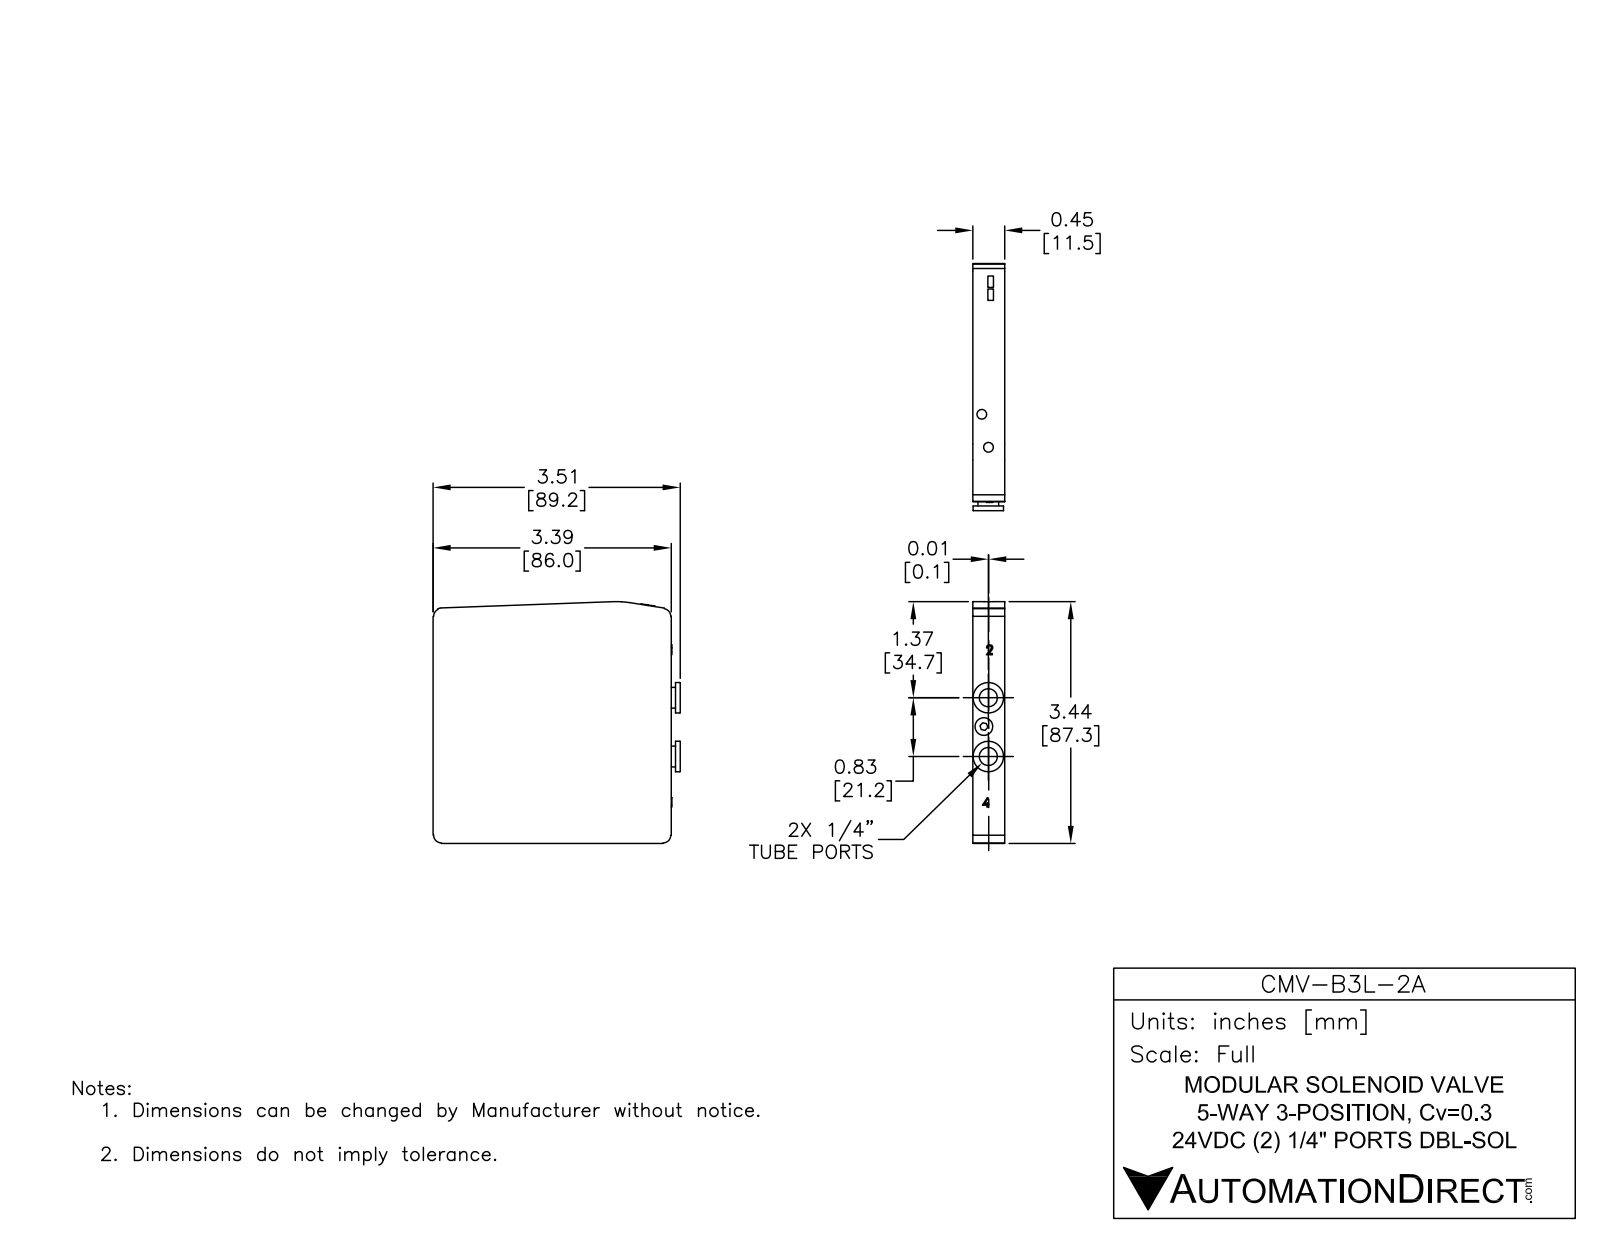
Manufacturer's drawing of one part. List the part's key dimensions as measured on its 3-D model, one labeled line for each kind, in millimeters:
Part name (STEP PRODUCT): CMV-B3L-2A
STEP written by: SolidWorks 2013 (AUTOMOTIVE_DESIGN)
Units: millimetres
Bodies: 78 solids, 1157 faces (879 planar, 162 cylindrical, 116 other)
Overall size (bounding box): 89.5 × 87.3 × 20.43
Volume: 78 068 mm³ · Surface area: 44 224 mm²
Round holes (diameter × count): ⌀5.25 ×4, ⌀6.5 ×4, ⌀3.35 ×2, ⌀4.4 ×2, ⌀8 ×2, ⌀9.5 ×2, ⌀3.6 ×1, ⌀6.25 ×1, ⌀6.4 ×1
Round bosses / shafts (diameter × count): ⌀1.5 ×4, ⌀10.8 ×2, ⌀7.75 ×2, ⌀6.25 ×2, ⌀5.75 ×2, ⌀4.2 ×2, ⌀4 ×2, ⌀3.5 ×1
Partial cylindrical surfaces — rounded edges, fillets, slot ends (radius × count): R2.35 ×12, R0.78 ×4, R1.5 ×4, R2.8 ×4, R0.15 ×2, R0.25 ×2, R1 ×2, R2.25 ×2
Main face-to-face distances: 11.5, 1.5, 10, 1, 3, 83, 2.5, 12.5, 10.83, 11.83
Hole centre spacings: 9.7, 19.83, 22.17, 8.66, 8.68, 9.46, 10.38, 10.63
